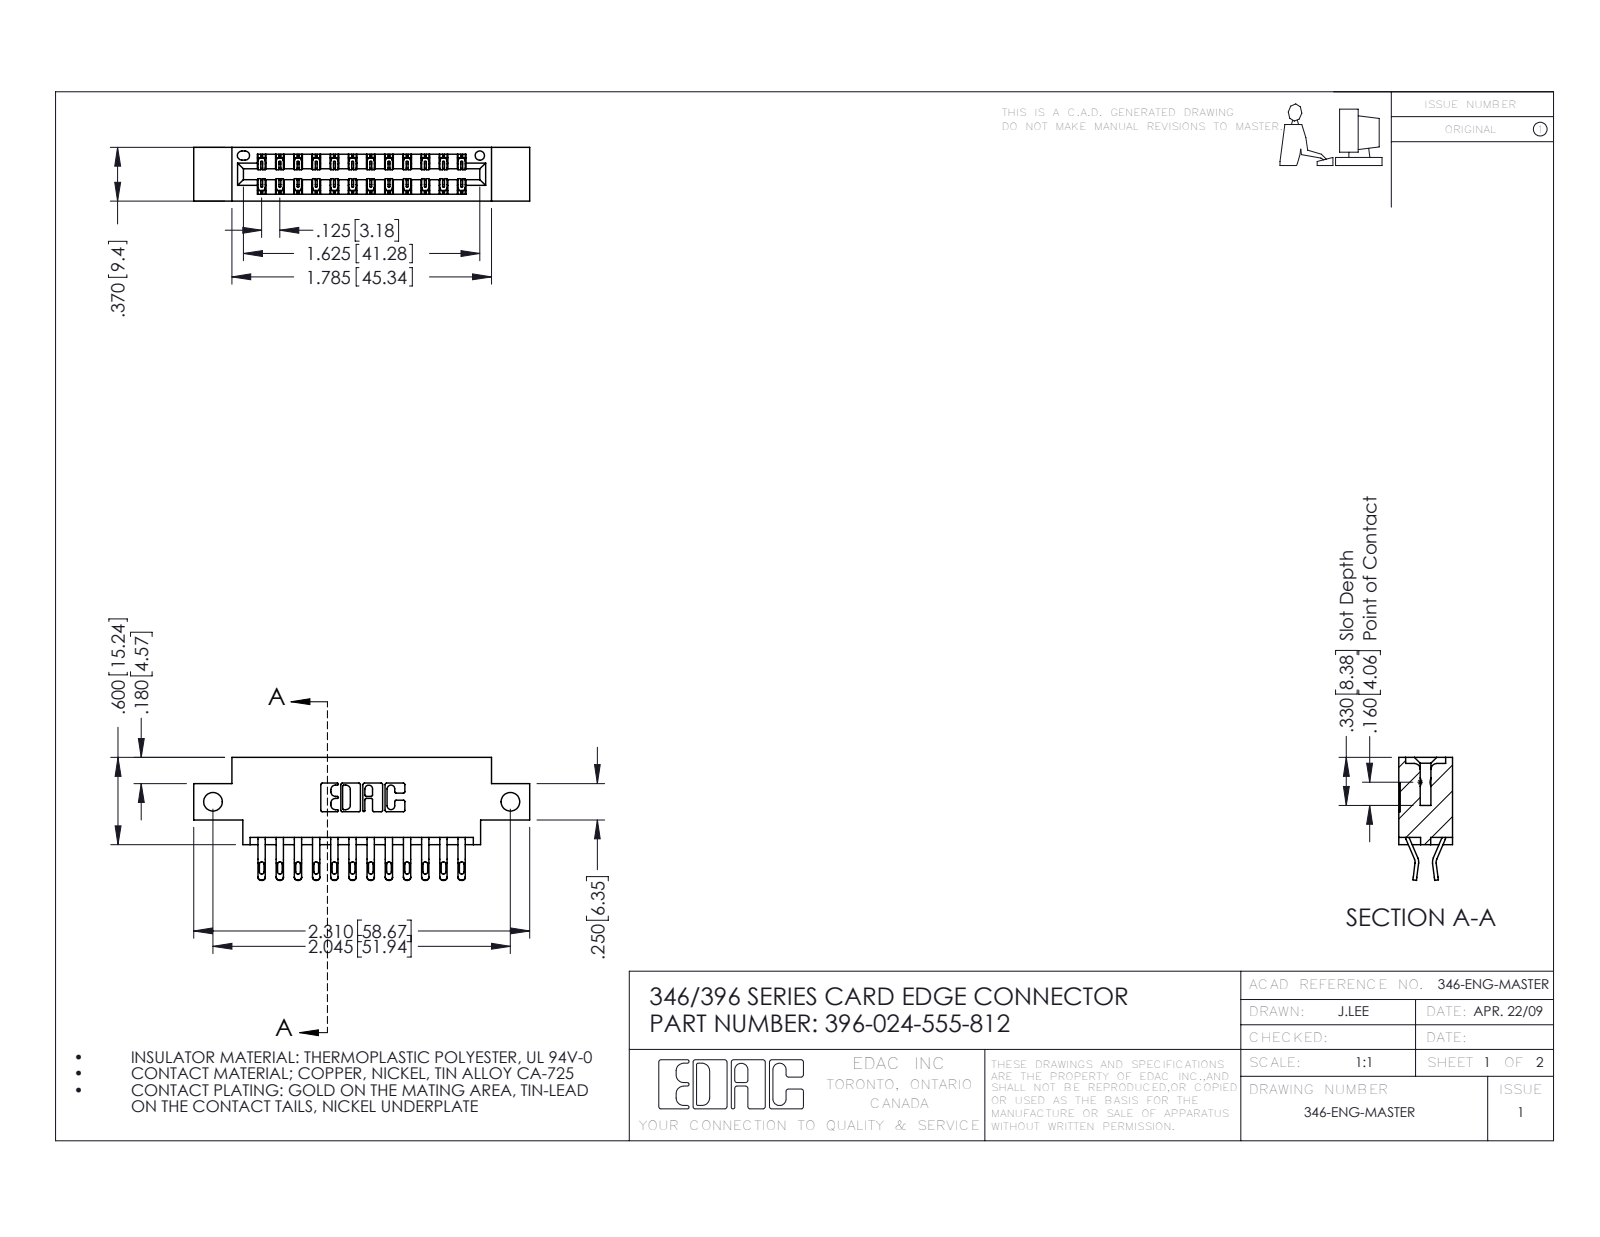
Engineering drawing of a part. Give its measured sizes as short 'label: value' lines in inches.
name: 345-292-001_555 Tail; 346 Part_0.170 Offset - Side Mount; 396-024-555-812
written by: SolidWorks 2016 (CONFIG_CONTROL_DESIGN)
unit: in
bodies: 25 solids, 1518 faces (872 planar, 646 cylindrical, 0 other)
size: 2.31 × 0.845 × 0.37
volume: 0.324 in³; area: 11.05 in²
holes: 2× ⌀0.128, 1× ⌀0.064
rounds: 48× R0.016, 48× R0.02, 36× R0.006, 22× R0.01, 6× R0.007, 6× R0.031, 3× R0.026, 2× R0.01
face distances: 0.25, 0.37, 0.048, 0.322, 0.025, 0.072, 0.298, 0.275, 0.148, 0.222
hole spacings: 2.045
